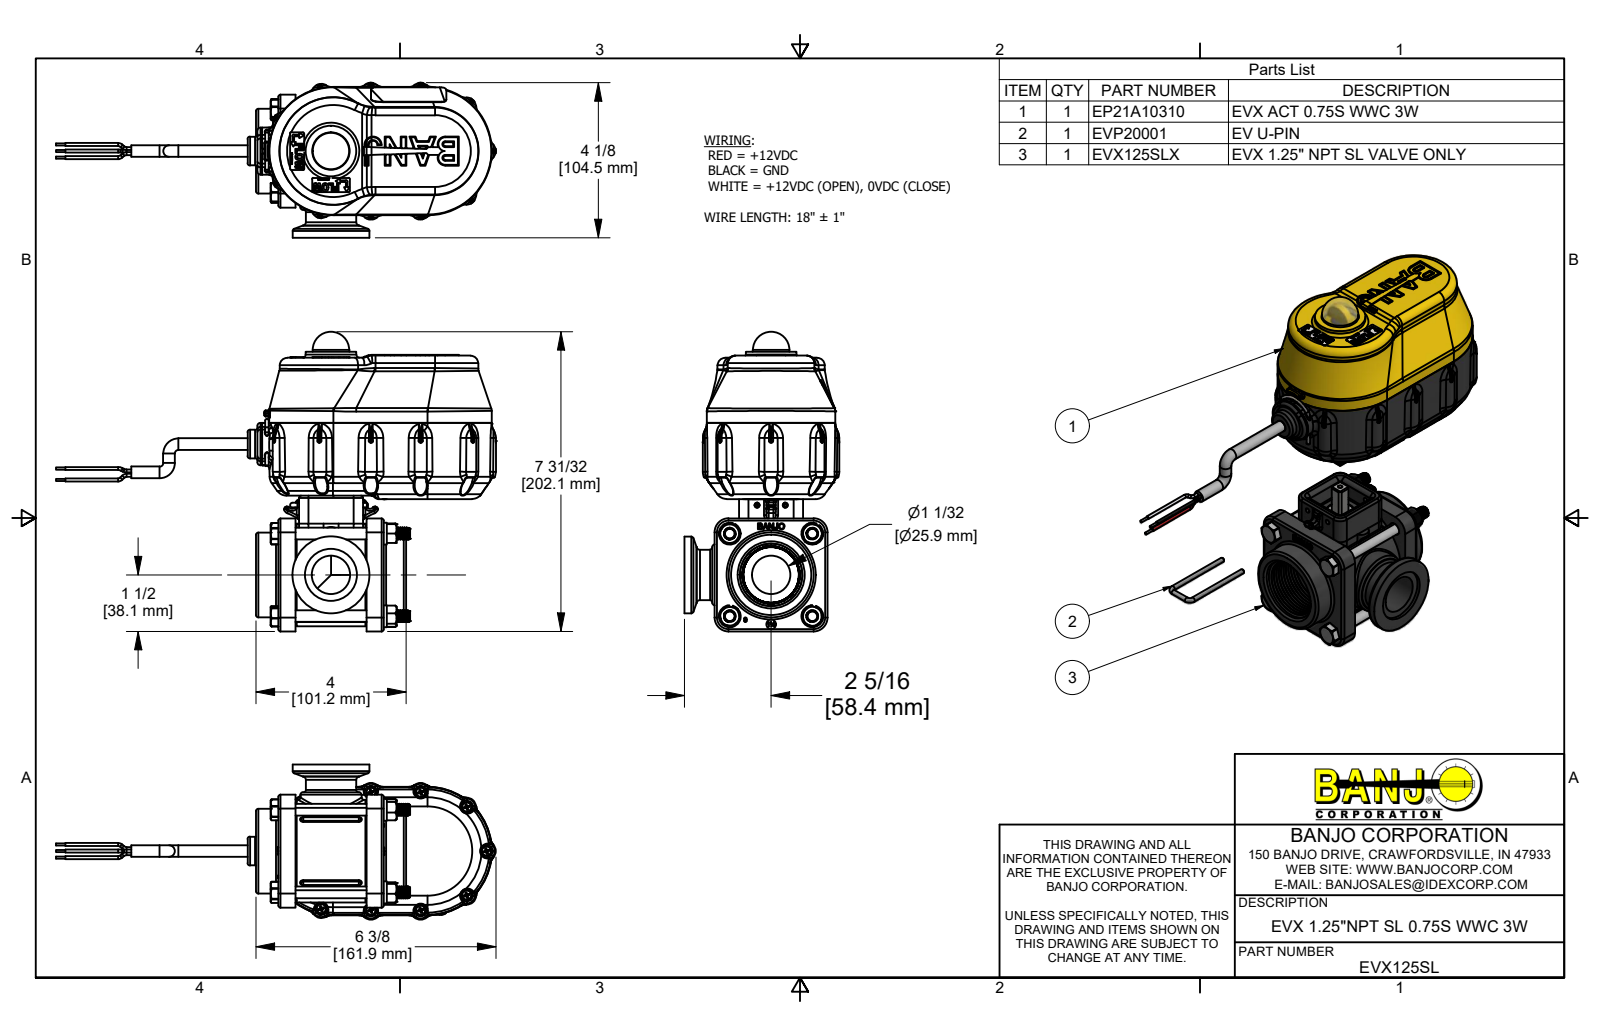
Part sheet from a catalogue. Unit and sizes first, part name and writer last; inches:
Units: inches
Overall size (bounding box): 49.551 × 7.957 × 4.115
Round holes (diameter × count): ⌀0.095 ×11, ⌀0.15 ×11, ⌀0.08 ×7, ⌀0.107 ×4, ⌀0.126 ×4, ⌀0.136 ×4, ⌀0.148 ×4, ⌀0.15 ×4, ⌀0.17 ×4, ⌀0.252 ×4, ⌀0.322 ×4, ⌀0.35 ×4
Round bosses / shafts (diameter × count): ⌀0.268 ×60, ⌀0.25 ×17, ⌀0.08 ×15, ⌀0.14 ×11, ⌀0.108 ×11, ⌀0.085 ×11, ⌀0.058 ×6, ⌀0.313 ×5
Partial cylindrical surfaces — rounded edges, fillets, slot ends (radius × count): R0.013 ×180, R0.04 ×145, R0.01 ×84, R0.02 ×72, R0.06 ×58, R0.005 ×53, R0.03 ×38, R0.08 ×28
Main face-to-face distances: 0.1, 2.565, 0.055, 0.211, 0.06, 0.151, 0.46, 2.345, 0.125, 0.045
Hole centre spacings: 1.55, 2.192, 2.656, 1.046, 1.513, 1.662, 1.891, 2.69
Volume: 51.03 in³ · Surface area: 868.6 in²
Bodies: 98 solids, 12157 faces (3320 planar, 3483 cylindrical, 5354 other)
Part name (STEP PRODUCT): EVX125SL; EP21A10310; EP10310; IRF4905 (+8 more)
STEP written by: Autodesk Inventor 2019 (AUTOMOTIVE_DESIGN)
